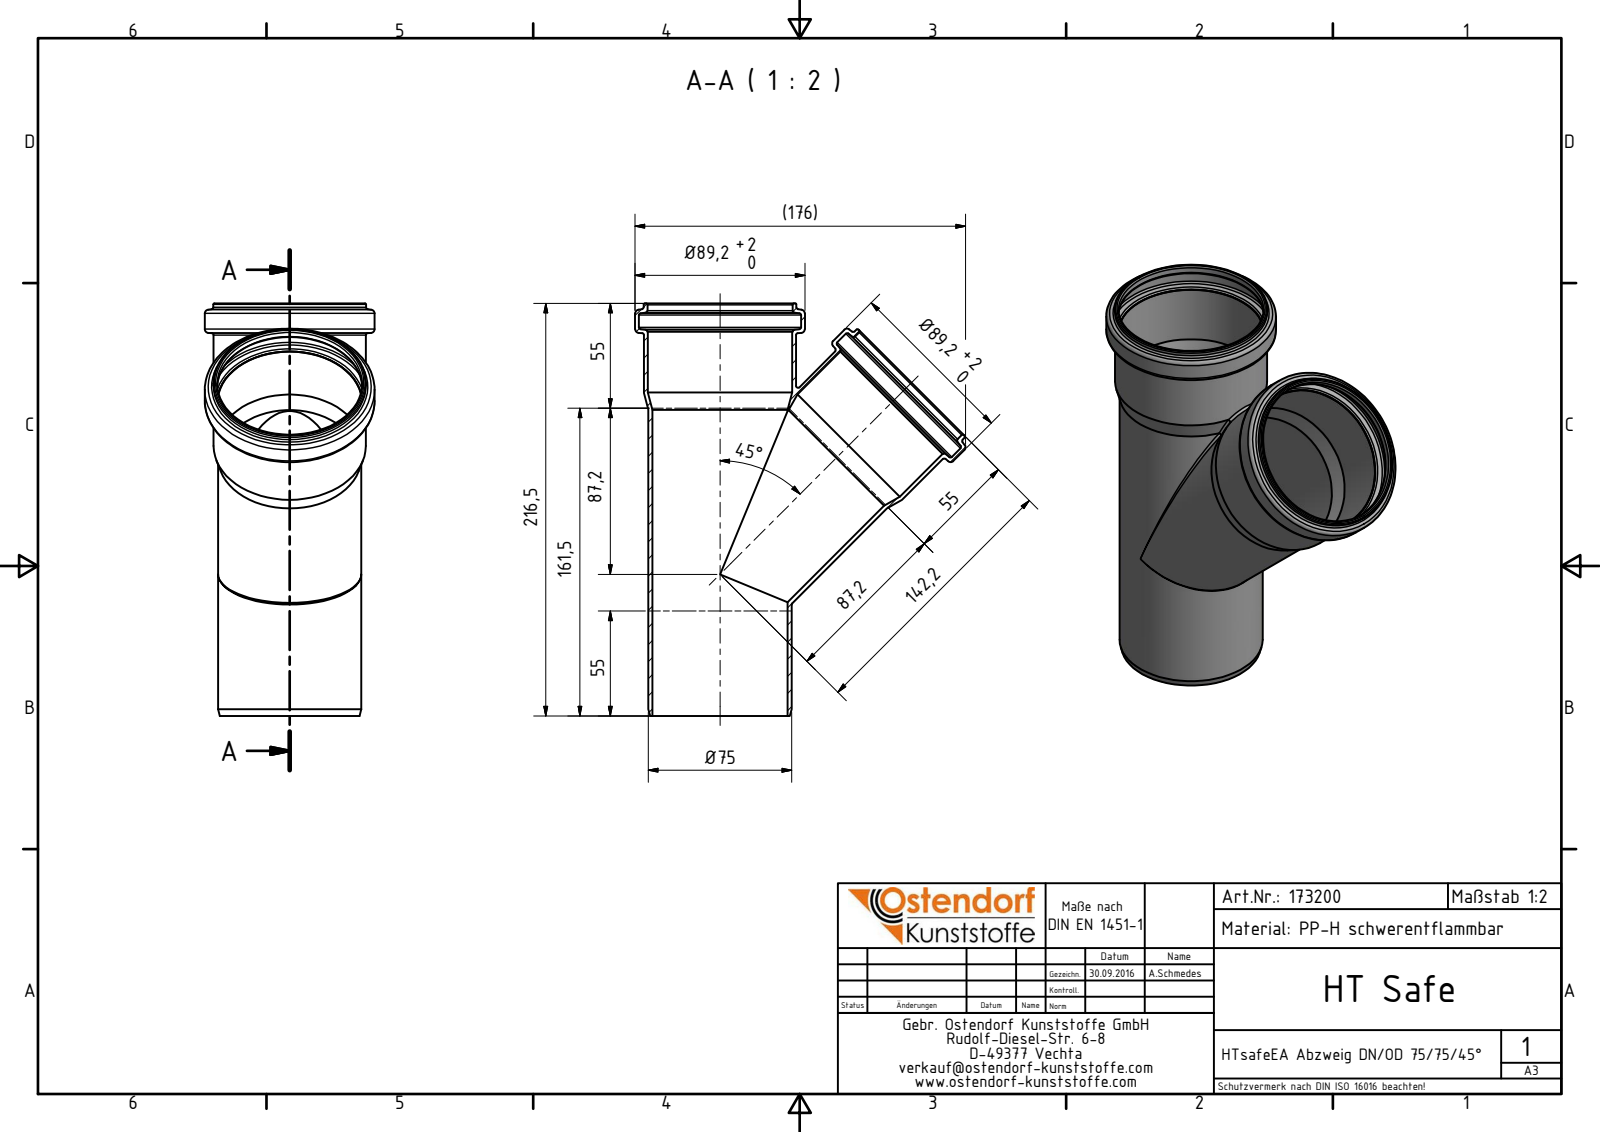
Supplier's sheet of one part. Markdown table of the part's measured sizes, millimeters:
| quantity | value |
| --- | --- |
| part name | 173200 HTsafeEA DN_OD 75_75_45° |
| STEP written by | Autodesk Inventor 2016 (AUTOMOTIVE_DESIGN) |
| units | millimeters |
| bodies | 1 solid, 62 faces (5 planar, 18 cylindrical, 39 other) |
| overall size | 216.5 × 173.54 × 89.2 |
| volume | 150 680 mm³ |
| surface area | 146 526 mm² |
| round holes (diameter × count) | 71 × 2, 75.9 × 2, 76.2 × 2, 85.2 × 2 |
| round bosses / shafts (diameter × count) | 89.2 × 2, 80.2 × 2, 79.9 × 2, 75.2 × 2 |
| main face-to-face distances | 216.5, 14.89, 201.61 |
